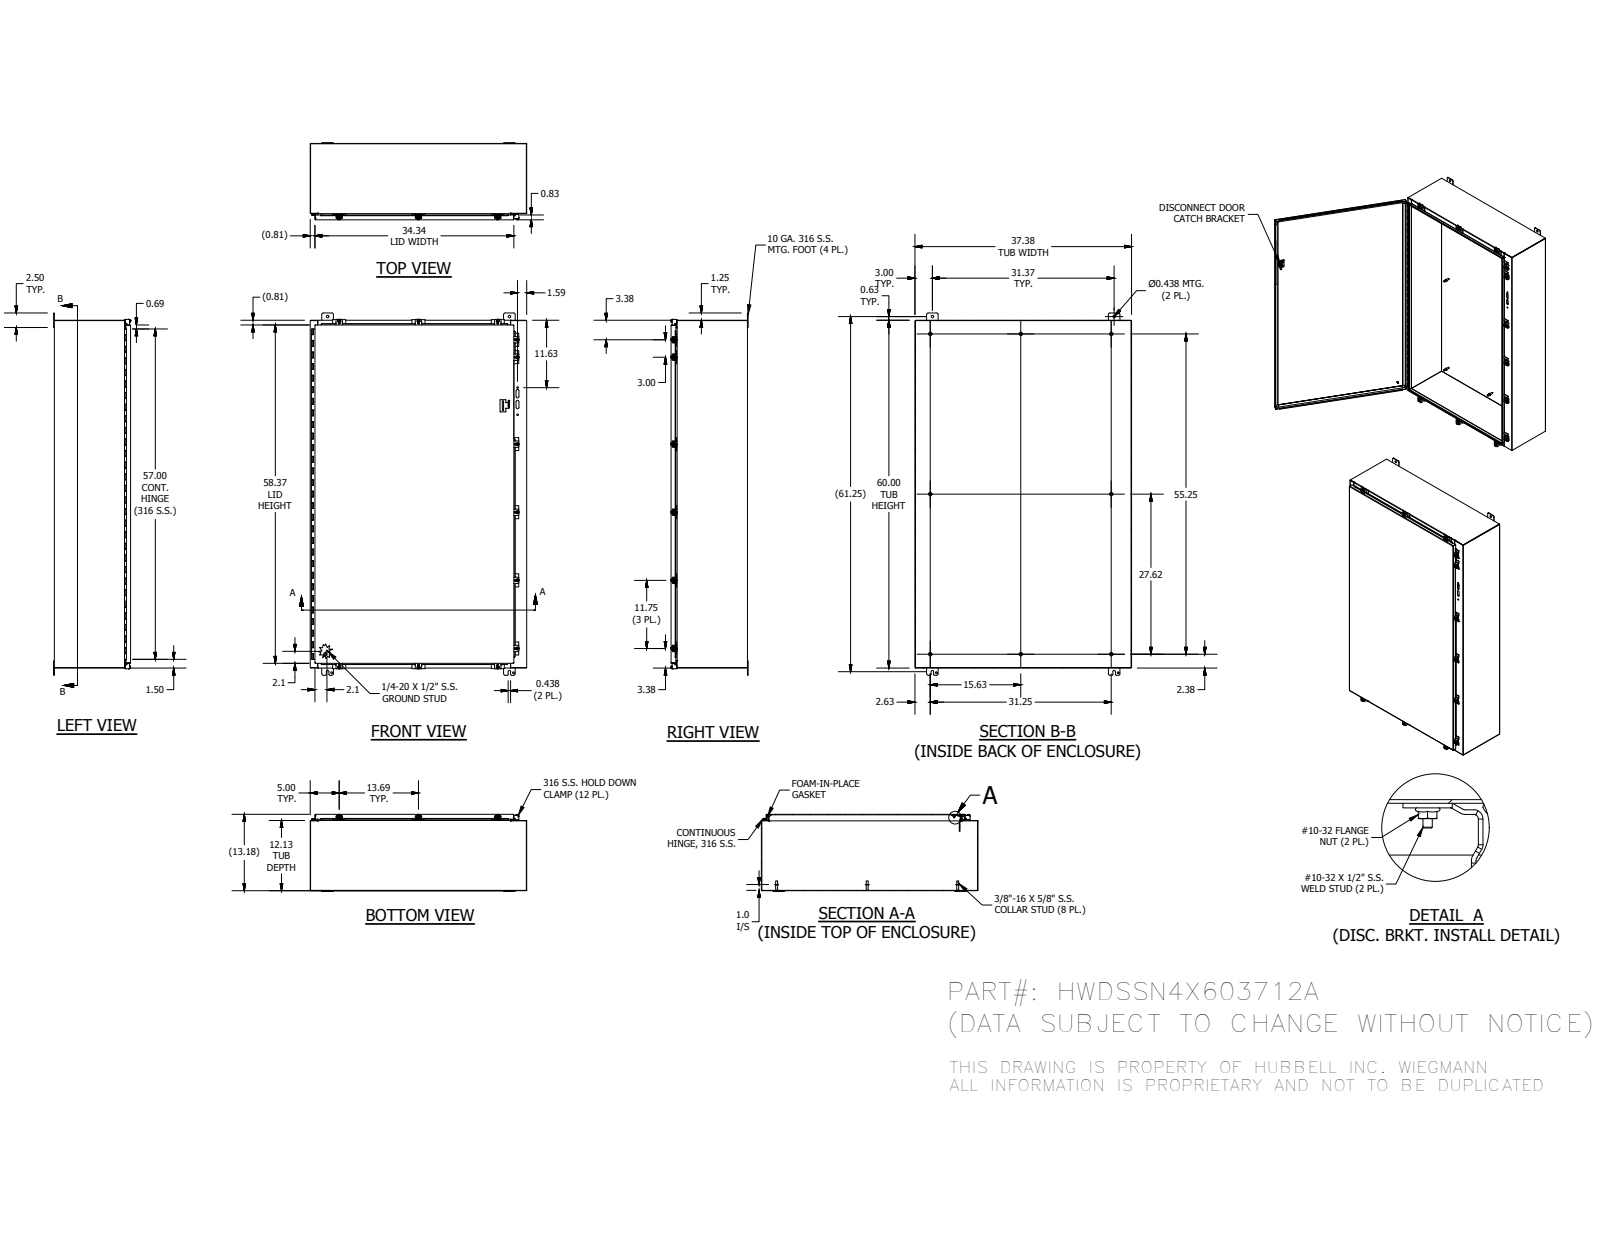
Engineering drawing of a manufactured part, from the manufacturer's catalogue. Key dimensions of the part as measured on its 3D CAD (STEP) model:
Part name (STEP PRODUCT): SSN4X603712ABLR; 38859; 34839; SSN4X6037ALID (+8 more)
STEP written by: Autodesk Inventor 2016 (AUTOMOTIVE_DESIGN)
Units: millimetres
Bodies: 26 solids, 1098 faces (685 planar, 343 cylindrical, 70 other)
Overall size (bounding box): 1587.5 × 949.33 × 337.85
Volume: 9 447 000 mm³ · Surface area: 9 764 000 mm²
Round holes (diameter × count): ⌀7.95 ×4, ⌀11.13 ×4, ⌀3.96 ×2, ⌀7.14 ×2, ⌀3.17 ×1
Round bosses / shafts (diameter × count): ⌀15.88 ×8, ⌀8.38 ×8, ⌀8.56 ×3, ⌀6.35 ×2, ⌀4.83 ×2, ⌀3.05 ×1
Partial cylindrical surfaces — rounded edges, fillets, slot ends (radius × count): R0.79 ×25, R2.67 ×21, R6.35 ×21, R3.17 ×11, R0.25 ×8, R1.92 ×8, R2.38 ×5, R4.76 ×5
Main face-to-face distances: 1.88, 332.79, 330.91, 334.67, 1522.12, 1.87, 945.57, 947.45, 949.32, 947.44
Hole centre spacings: 40.46, 796.92, 1524, 1719.78, 780.32, 815.19, 1487.6, 1560.6
